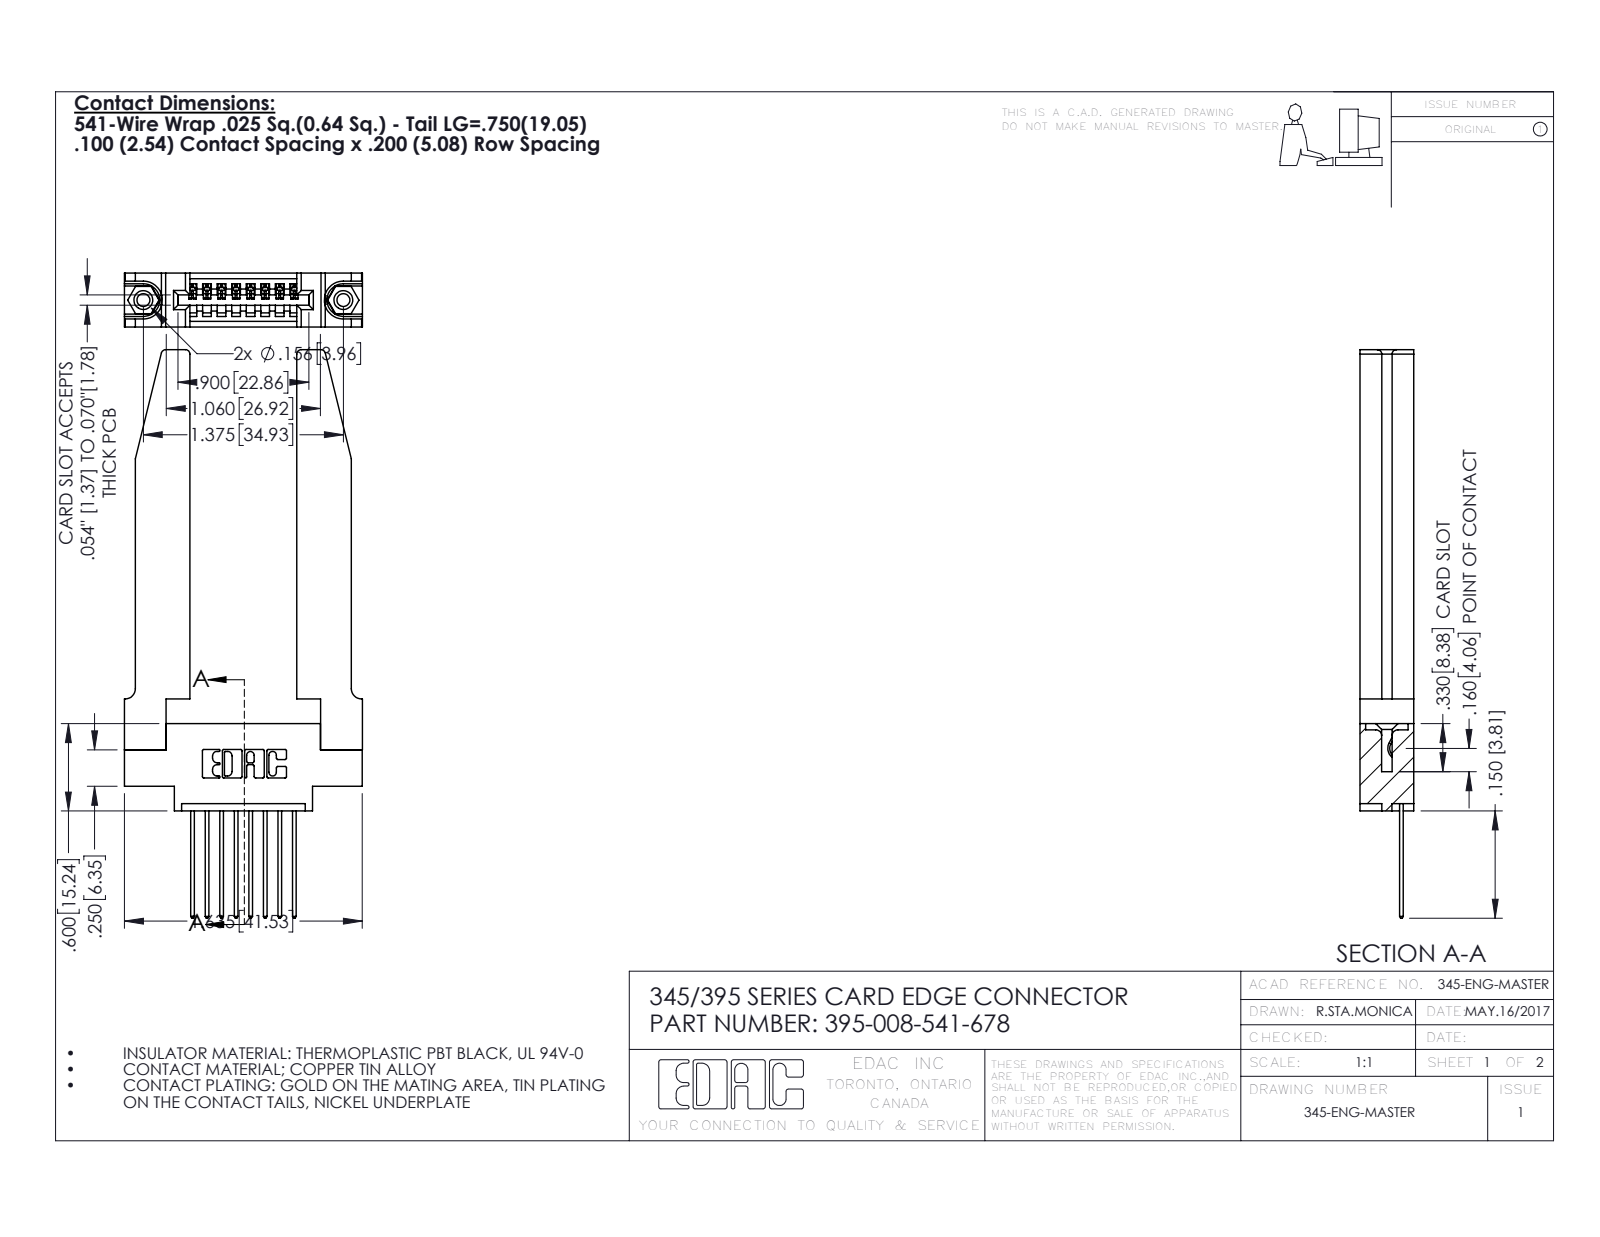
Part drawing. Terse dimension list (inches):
name: 345 Part_0.170 Offset - 0.156 Dia-TH; 345-220-078_345-220-078; 345-292-001_345-293-141; 395-008-541-678 (+1 more)
written by: SolidWorks 2016 (CONFIG_CONTROL_DESIGN)
unit: in
bodies: 13 solids, 828 faces (546 planar, 230 cylindrical, 52 other)
size: 3.907 × 1.636 × 0.37
volume: 0.693 in³; area: 17.71 in²
holes: 2× ⌀0.089, 2× ⌀0.125, 2× ⌀0.156, 1× ⌀0.064
bosses: 2× ⌀0.155
rounds: 22× R0.01, 16× R0.006, 16× R0.01, 8× R0.03, 6× R0.007, 6× R0.031, 3× R0.026, 2× R0.031
face distances: 0.37, 0.072, 0.298, 0.15, 0.22, 0.148, 0.735, 0.077, 0.123, 0.095
hole spacings: 0.27, 1.144, 1.375
